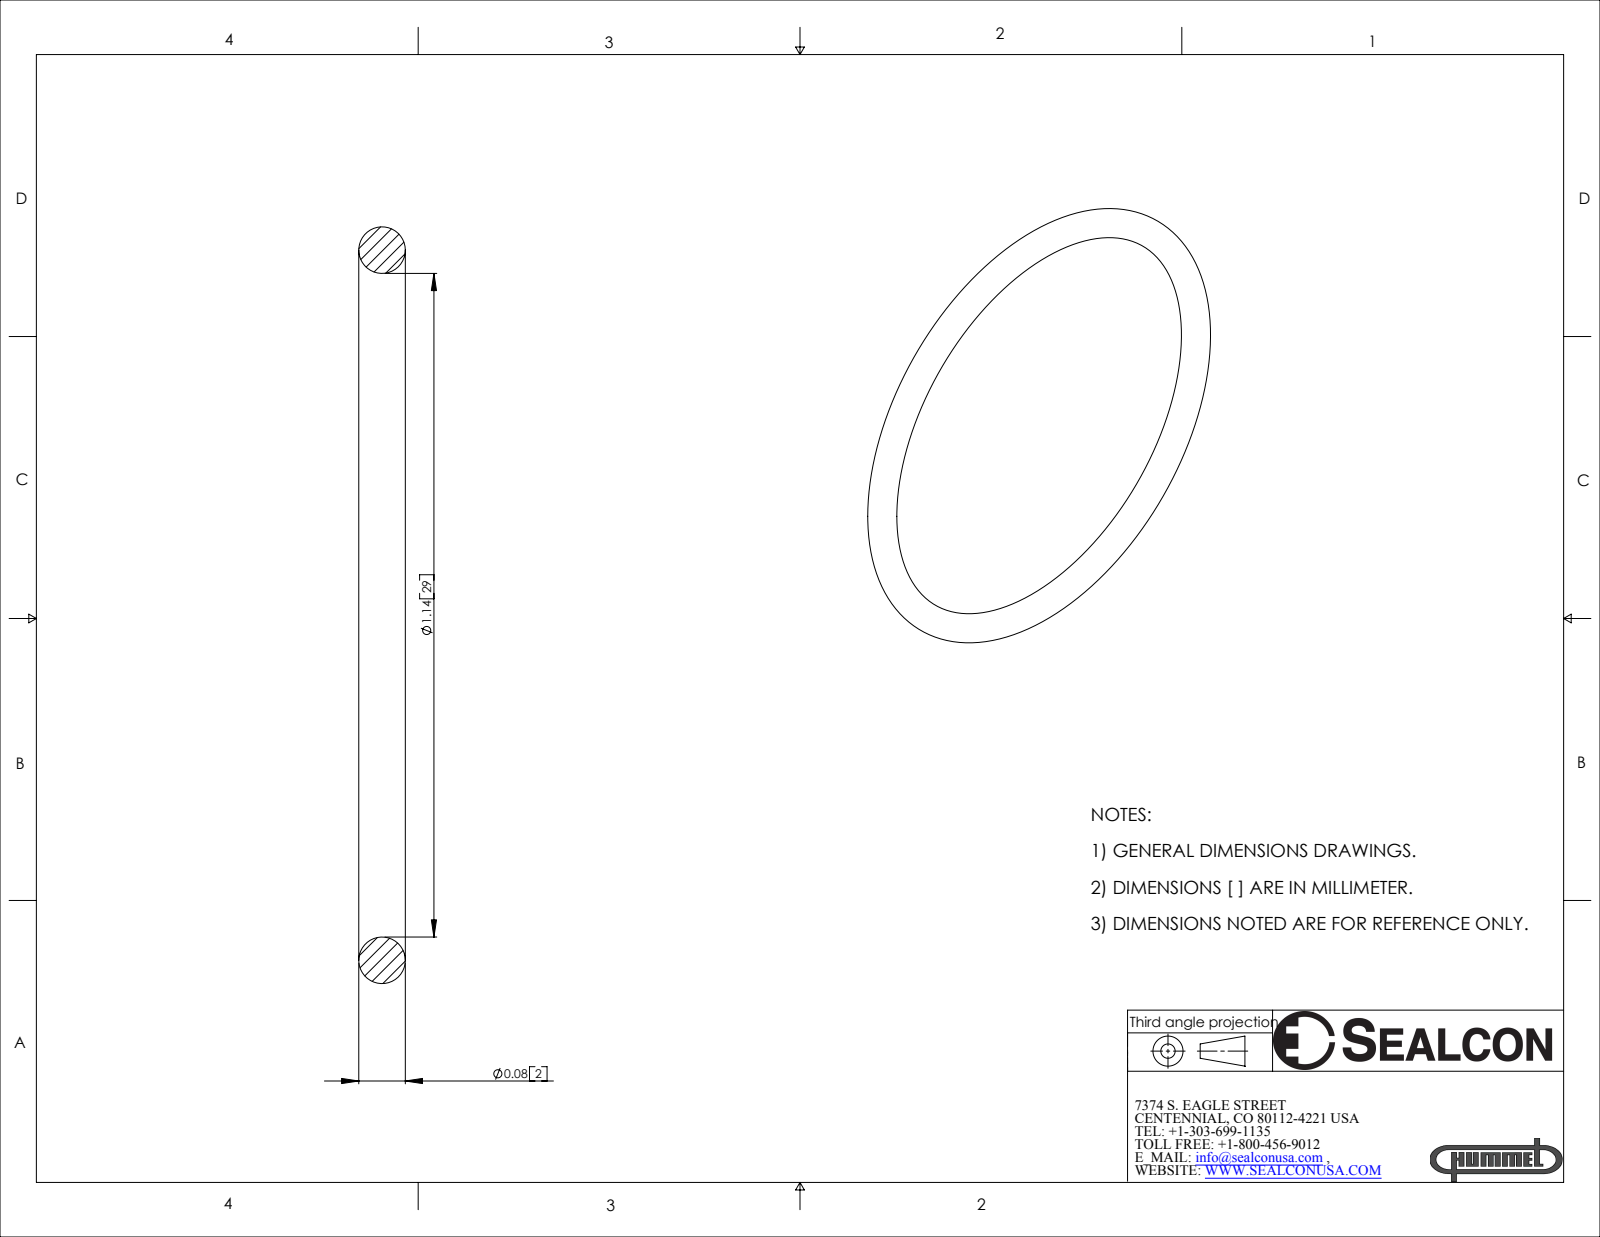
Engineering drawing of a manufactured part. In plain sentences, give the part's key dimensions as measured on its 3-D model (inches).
The part is named "OR-10-BN". Its 3-D file was written by "SolidWorks 2007 (CONFIG_CONTROL_DESIGN)". It is 1 solid with 4 faces: 0 planar, 0 cylindrical and 4 other. Overall it measures 1.3 by 1.3 by 0.08 inches. Its volume is 0.019 cubic inches and its surface area 0.963 square inches.
